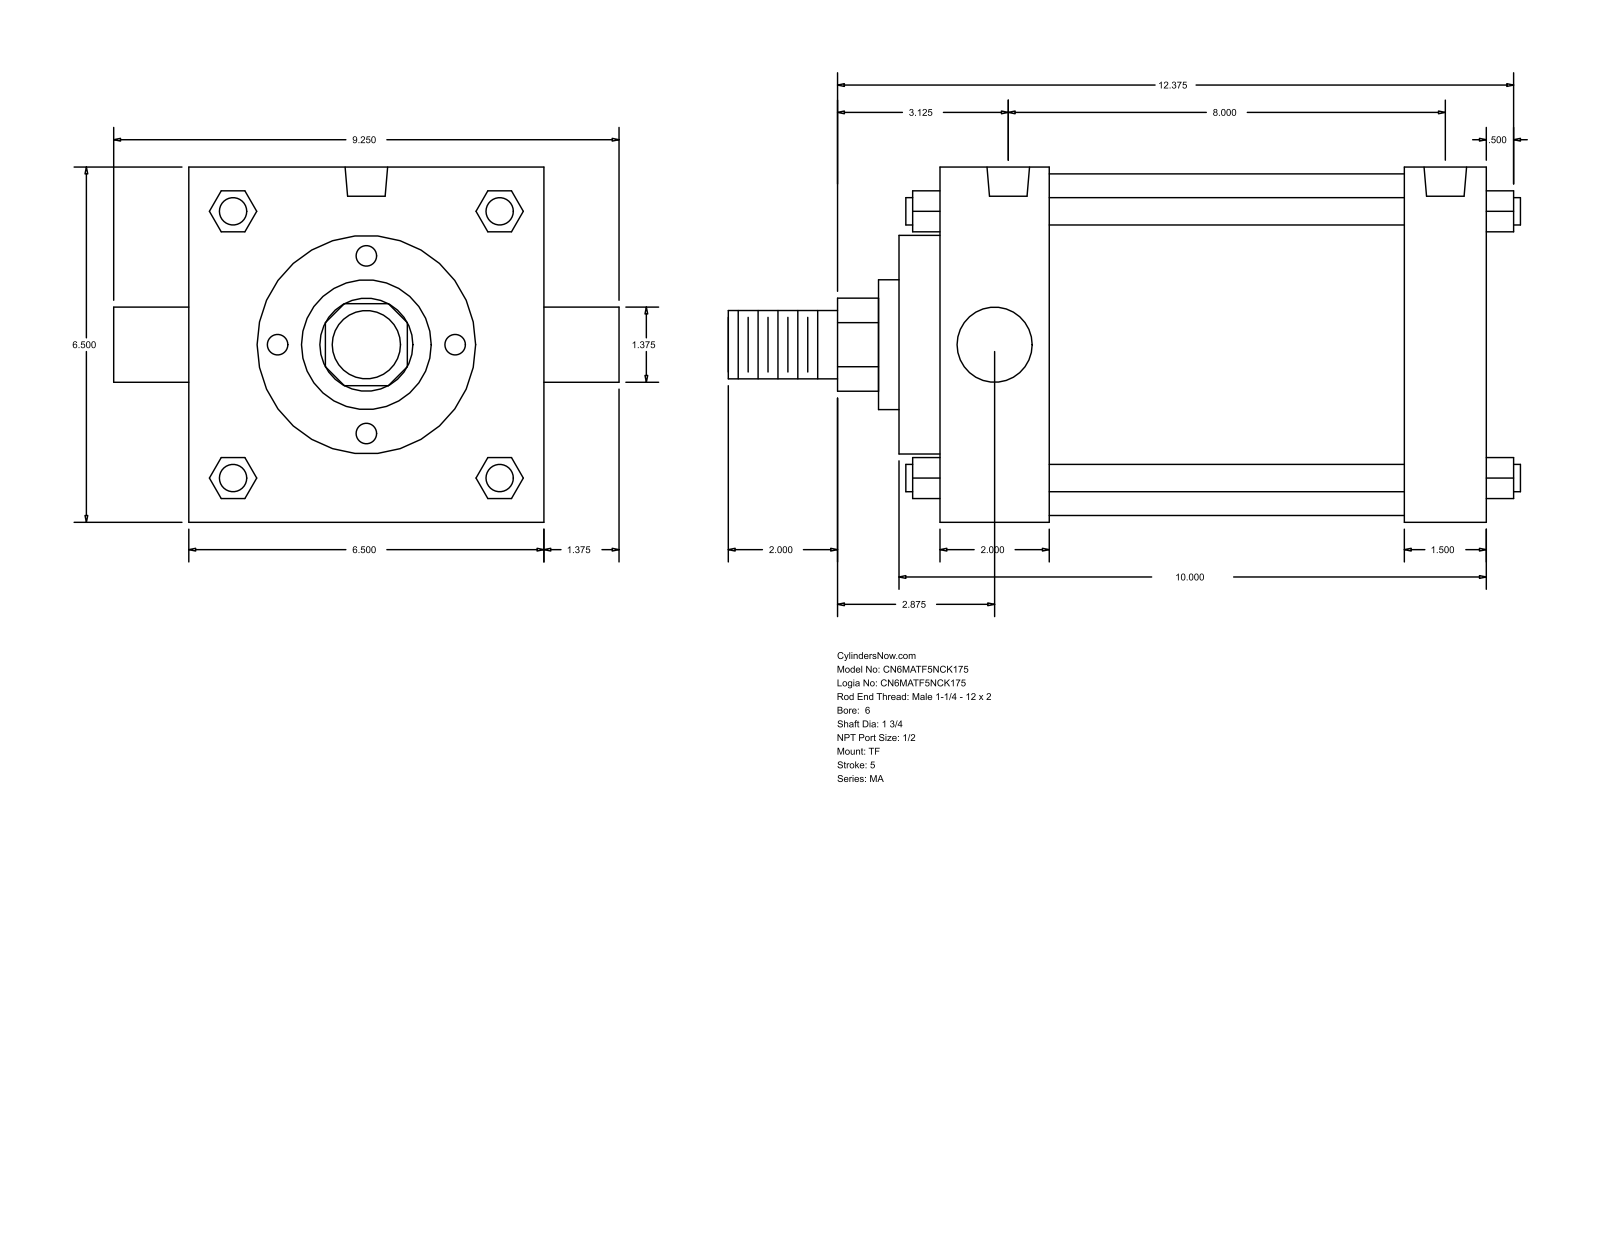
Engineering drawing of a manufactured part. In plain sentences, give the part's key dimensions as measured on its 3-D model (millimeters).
The part is named "MA_TF__0600_1.75". Its 3-D file was written by "GSSL Pune (CONFIG_CONTROL_DESIGN)". It is 0 solids with 122 faces: 93 planar, 29 cylindrical and 0 other. Overall it measures 368.3 by 234.95 by 165.1 millimeters. Round holes: 3 of diameter 17.46, 2 of diameter 19.77. Round bosses or shafts: 4 of diameter 12.7, 1 of diameter 158.75, 1 of diameter 101.6, 1 of diameter 60.33, 1 of diameter 44.45, 1 of diameter 34.92, 1 of diameter 31.75. Partial cylindrical surfaces (rounded edges, fillets, slot ends): 1 of radius 21.63. The main face-to-face distances are 165.1, 254, 19.05, 50.8, 215.9, 38.1, 203.2, 69.85, 234.95, 273.05. The hole center spacings are 203.19.
